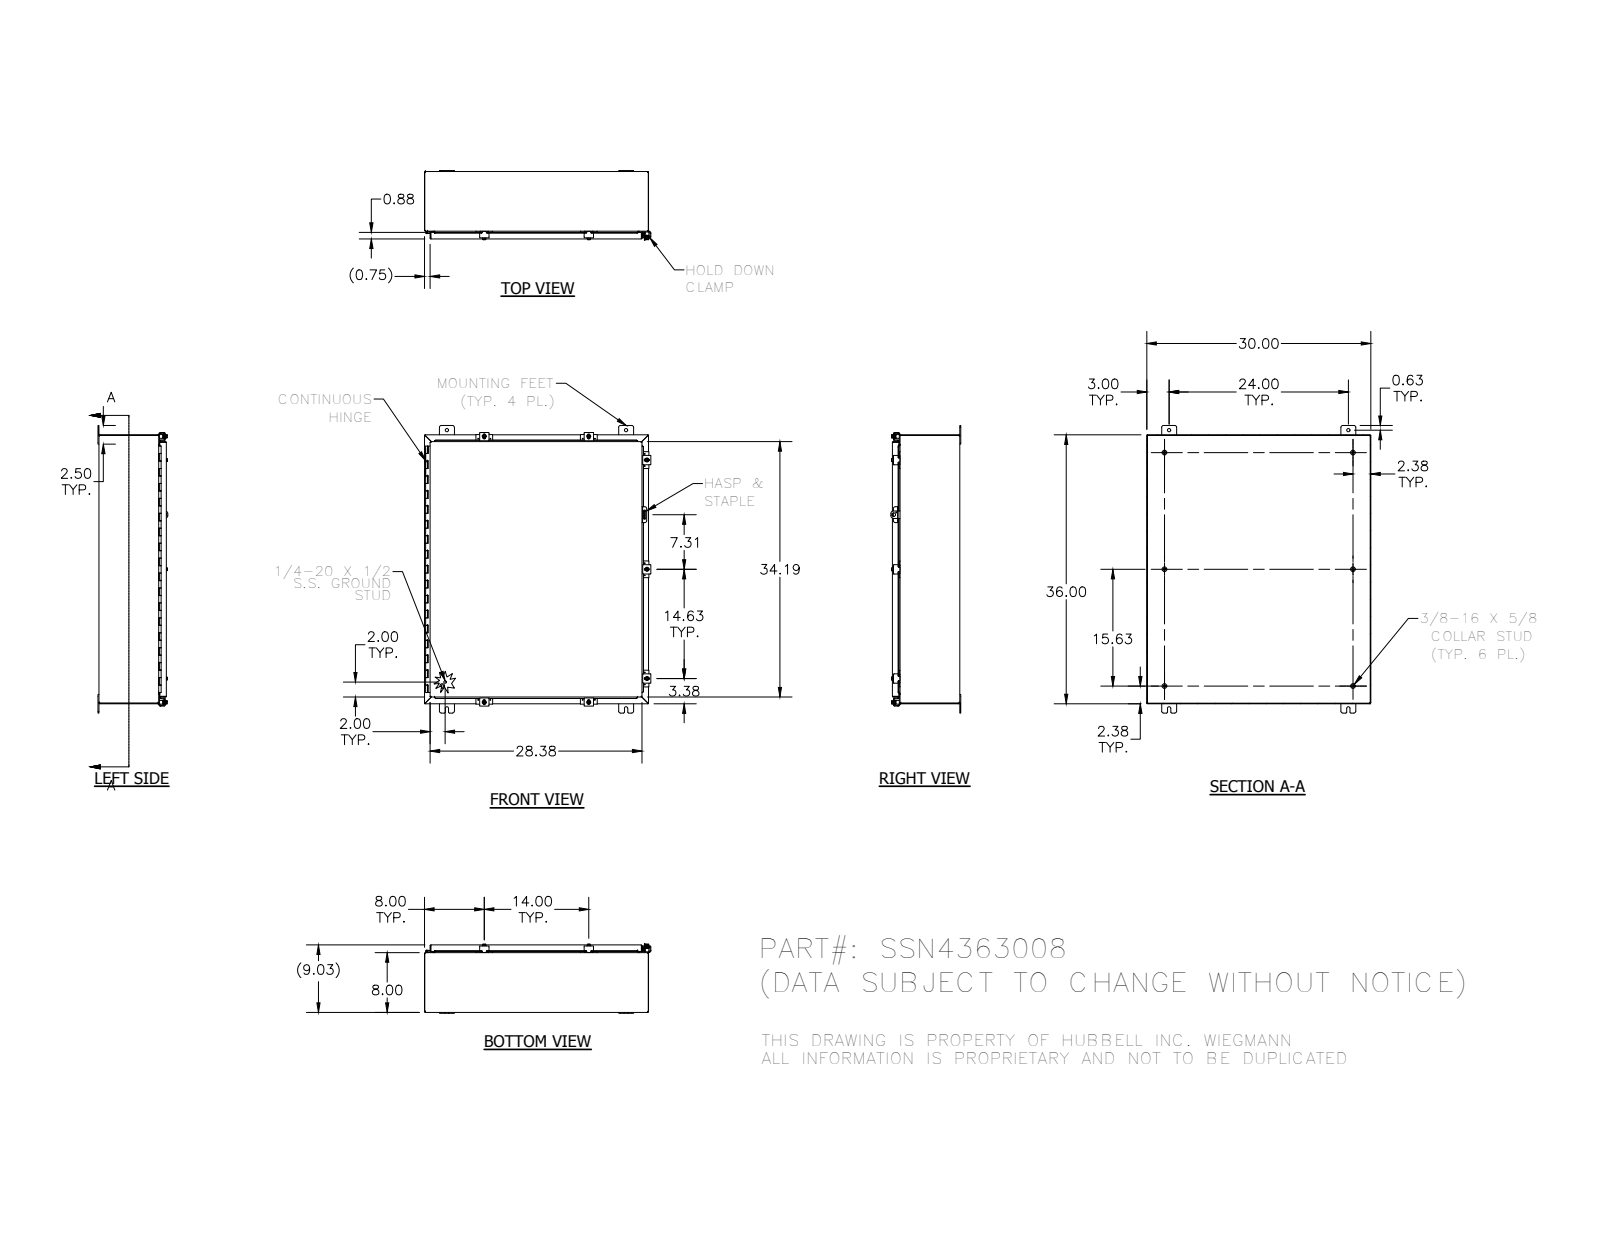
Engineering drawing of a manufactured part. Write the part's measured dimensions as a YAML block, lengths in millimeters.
part_name: "HFW30825-2; 34871; 328140L; SSN4363008 (+8 more)"
step_written_by: "SolidWorks 2014 (AUTOMOTIVE_DESIGN)"
units: millimeters
bodies: {solids: 54, faces: 2204, planar: 846, cylindrical: 983, other: 375}
overall_size: [977.9, 769.9, 237.6]
volume: 4642000
surface_area: 4818000
round_holes:
  - {diameter: 2.8, count: 14}
  - {diameter: 5.4, count: 7}
  - {diameter: 7.1, count: 7}
  - {diameter: 7.6, count: 7}
  - {diameter: 11.1, count: 4}
  - {diameter: 3.2, count: 1}
  - {diameter: 4, count: 1}
  - {diameter: 12.7, count: 1}
round_bosses_or_shafts:
  - {diameter: 6.4, count: 9}
  - {diameter: 13.2, count: 7}
  - {diameter: 12.7, count: 7}
  - {diameter: 8.9, count: 7}
  - {diameter: 15.9, count: 6}
  - {diameter: 8.4, count: 6}
  - {diameter: 2.9, count: 2}
  - {diameter: 8.6, count: 1}
partial_cylinders:
  - {radius: 0.8, count: 83}
  - {radius: 3.2, count: 37}
  - {radius: 6.4, count: 33}
  - {radius: 0.8, count: 23}
  - {radius: 2.7, count: 23}
  - {radius: 1.6, count: 15}
  - {radius: 3.6, count: 14}
  - {radius: 2.5, count: 10}
face_to_face_distances: [1.9, 227.6, 225.7, 229.4, 760.1, 912.5, 201.3, 26.2, 758.2, 762]
hole_center_spacings: [22.3, 896.6, 355.6, 41.3, 335.1, 351, 371.5, 376.3]
